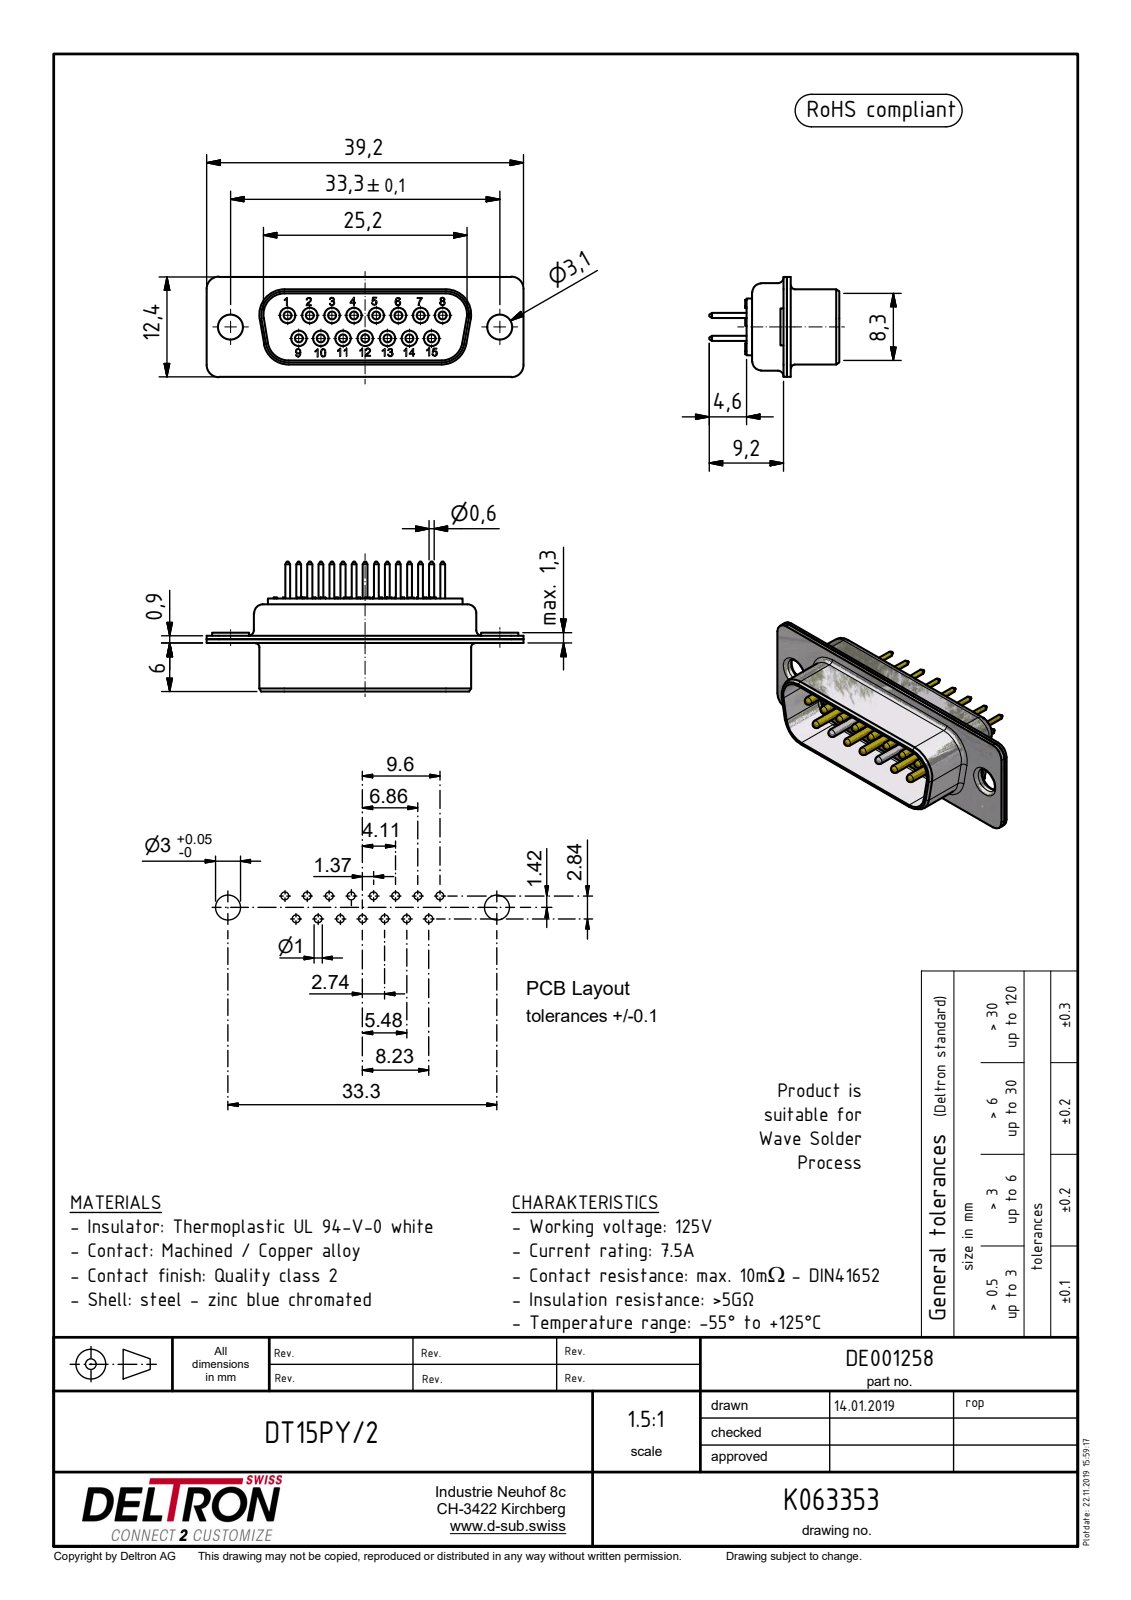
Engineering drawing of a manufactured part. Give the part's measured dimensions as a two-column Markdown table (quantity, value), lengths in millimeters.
| quantity | value |
| --- | --- |
| part name | K063353; N00403_BG; R+B00754_BG; R+B00153_BG (+1 more) |
| STEP written by | Autodesk Inventor 2018 (AUTOMOTIVE_DESIGN) |
| units | millimeters |
| bodies | 18 solids, 975 faces (466 planar, 251 cylindrical, 258 other) |
| overall size | 39.2 × 16.1 × 12.4 |
| volume | 1 614 mm³ |
| surface area | 4 552 mm² |
| round holes (diameter × count) | 1.92 × 15, 2.3 × 15, 0.34 × 2, 3.1 × 2, 4.06 × 2, 0.24 × 1, 0.28 × 1 |
| round bosses / shafts (diameter × count) | 2.23 × 15, 1.96 × 15, 1.94 × 15, 1.6 × 15, 1.6 × 15, 1 × 15, 0.6 × 15, 4.6 × 2 |
| partial cylindrical surfaces (radius × count) | 2 × 12, 0.25 × 8, 0.7 × 8, 1 × 8, 1.1 × 8, 0.5 × 4, 1.2 × 4, 1.5 × 4 |
| main face-to-face distances | 0.5, 0.4, 8.8, 0.65, 0.8, 8.3, 0.9, 0.6, 8.95, 9.45 |
| hole center spacings | 3.15, 2.74, 5, 5.48, 7.42, 8.22, 10, 10.96 |
